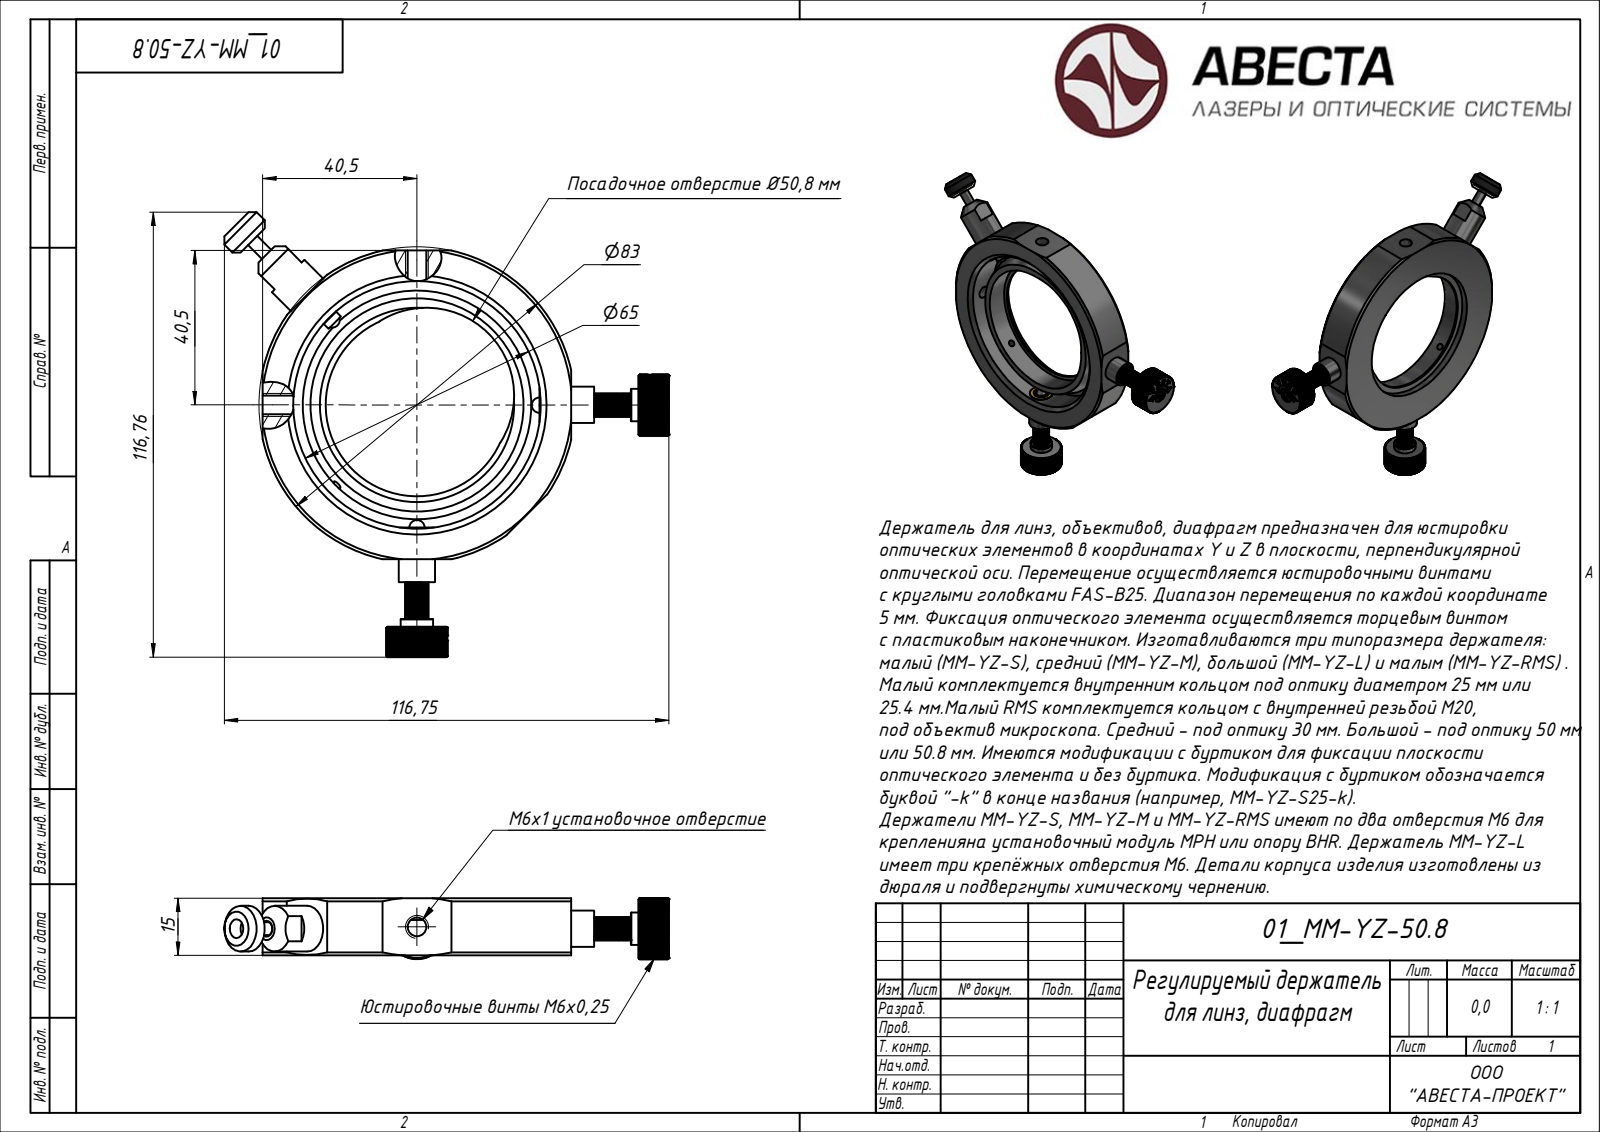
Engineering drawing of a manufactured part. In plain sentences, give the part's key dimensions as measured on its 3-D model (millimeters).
The part is named "01_MM-YZ-50.8". Its 3-D file was written by "ST-DEVELOPER v15 (AUTOMOTIVE_DESIGN)". It is 28 solids with 1154 faces: 529 planar, 0 cylindrical and 625 other. Overall it measures 259.38 by 119.03 by 18.53 millimeters. Its volume is 90 350 cubic millimeters and its surface area 51 480 square millimeters. The main face-to-face distances are 2.5, 15, 15.05, 12.5, 2.54, 12.51, 8, 2.51, 12.54, 80.99.
